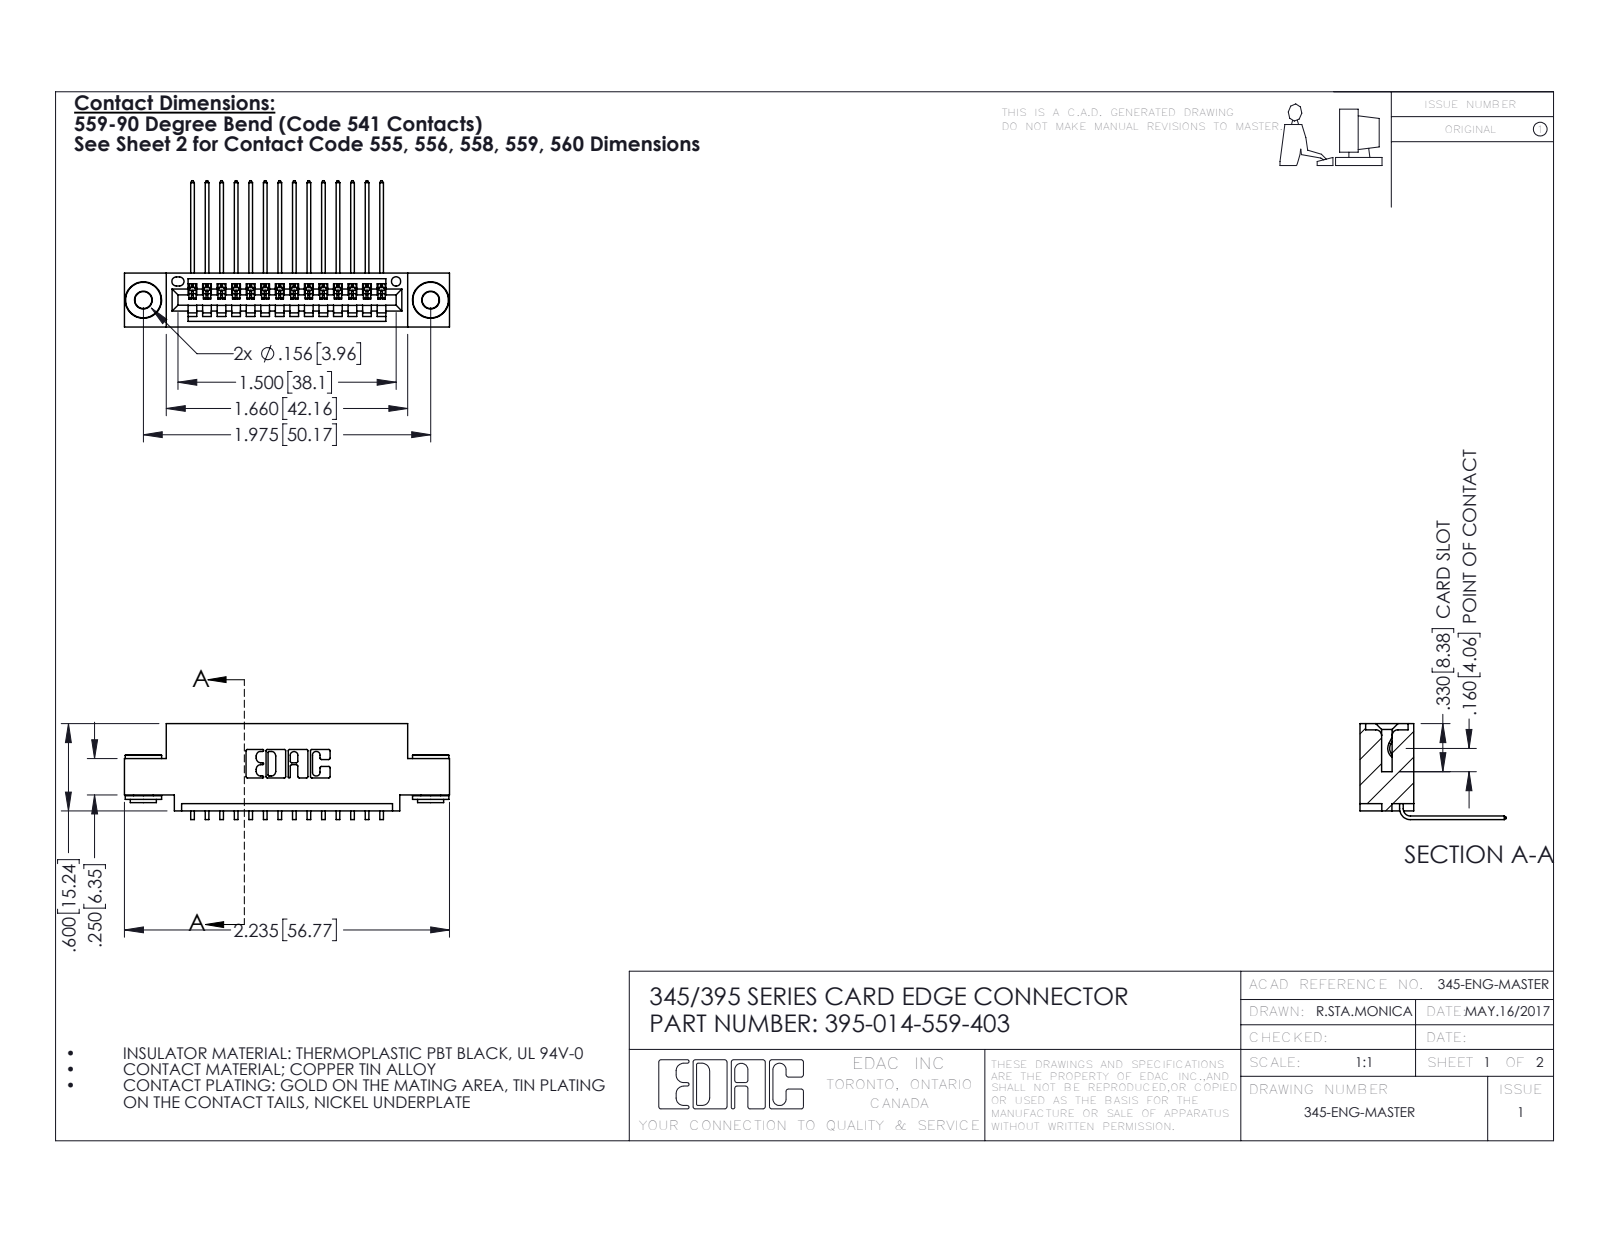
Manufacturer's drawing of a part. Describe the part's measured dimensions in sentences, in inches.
The part is named "345 Part_0.110 Offset - 0.156 Dia-TH; 395-014-559-403; 345-250-002_345-250-002-102; 345-292-001_558 559 Tail - 1". Its 3-D file was written by "SolidWorks 2016 (CONFIG_CONTROL_DESIGN)". It is 17 solids with 1008 faces: 682 planar, 318 cylindrical and 8 other. Overall it measures 2.235 by 1.005 by 0.659 inches. Its volume is 0.315 cubic inches and its surface area 10.91 square inches. Round holes: 2 of diameter 0.116, 2 of diameter 0.156, 1 of diameter 0.064. Round bosses or shafts: 2 of diameter 0.25, 2 of diameter 0.18, 2 of diameter 0.136. Partial cylindrical surfaces (rounded edges, fillets, slot ends): 28 of radius 0.006, 22 of radius 0.01, 6 of radius 0.007, 6 of radius 0.031, 3 of radius 0.026, 2 of radius 0.031, 2 of radius 0.04, 1 of radius 0.014. The main face-to-face distances are 0.072, 0.298, 0.37, 0.2, 0.025, 0.098, 0.272, 0.225, 0.1, 0.3. The hole center spacings are 0.27, 1.742, 1.975.
